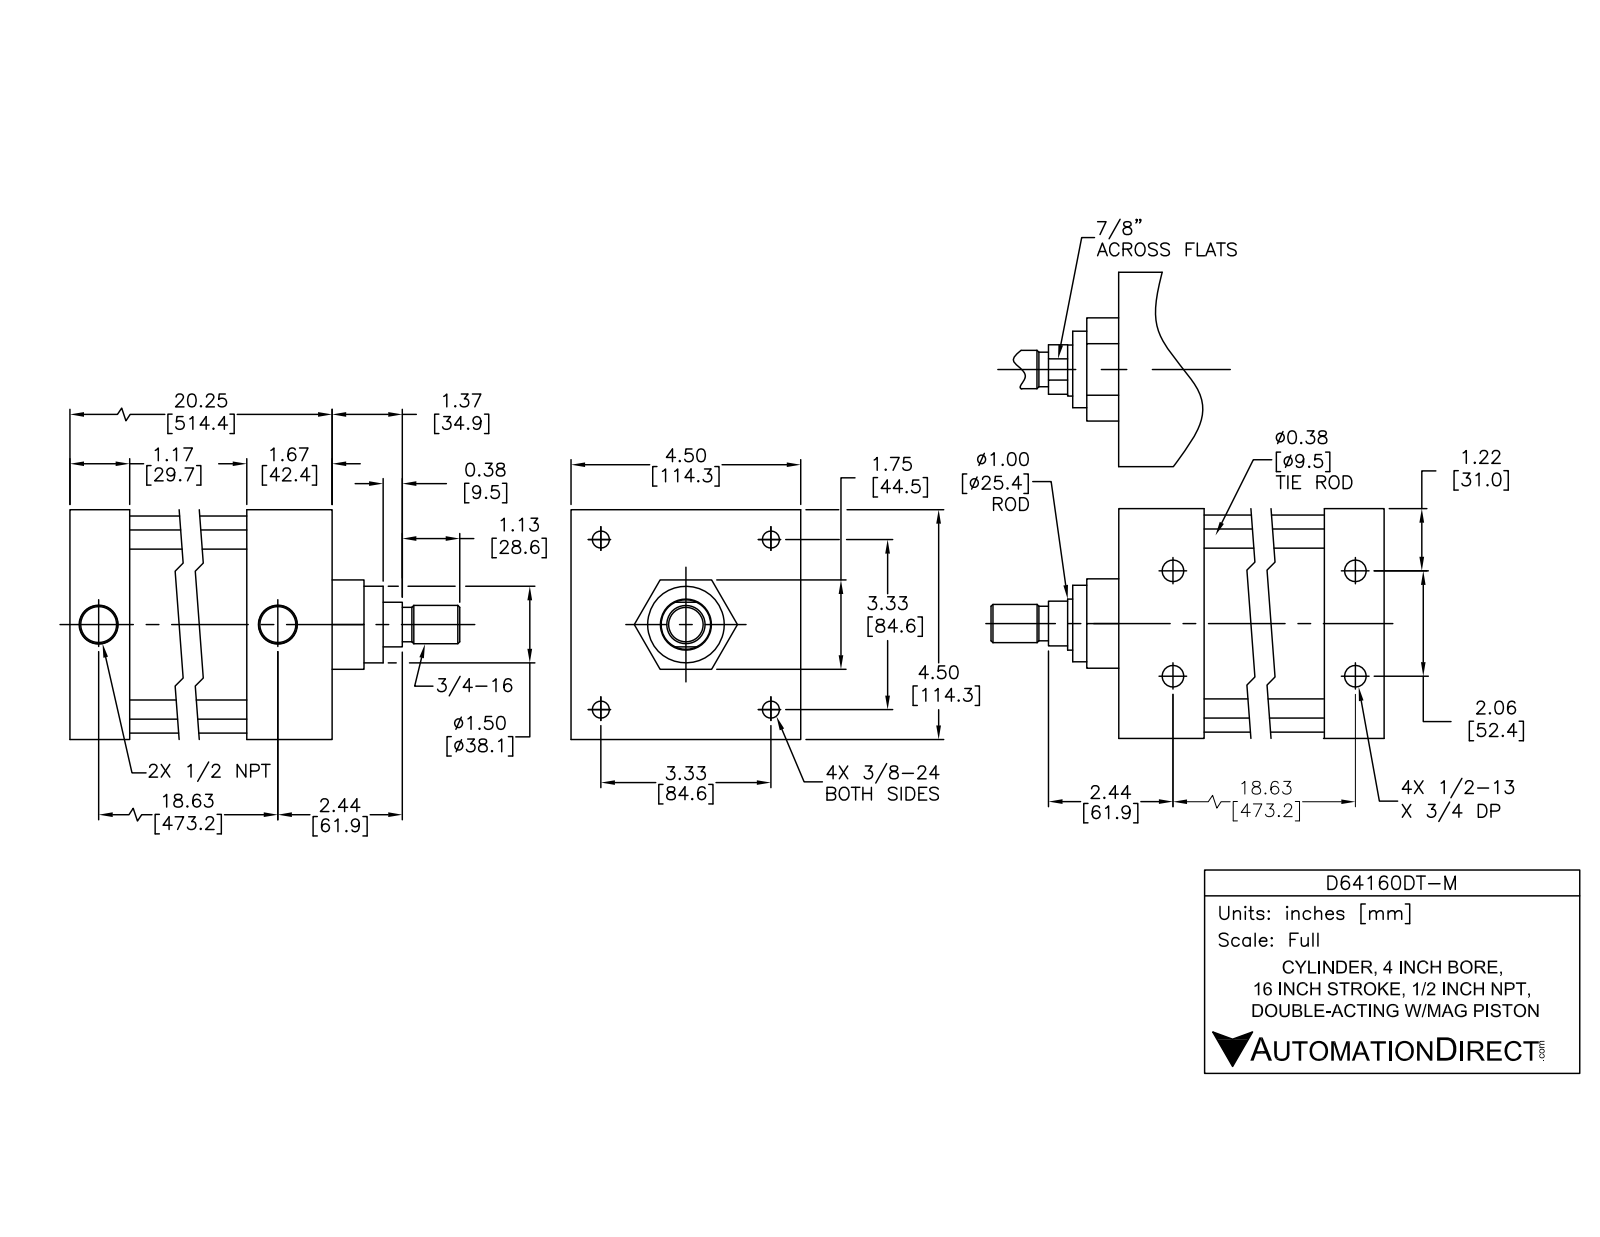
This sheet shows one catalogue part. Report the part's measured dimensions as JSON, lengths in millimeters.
{"part_name": "D64160DT-M; D64160DT-M PISTON; D64160DT-M BODY", "step_written_by": "SolidWorks 2015 (AUTOMOTIVE_DESIGN)", "units": "millimeters", "bodies": {"solids": 12, "faces": 303, "planar": 99, "cylindrical": 114, "other": 90}, "overall_size": [577.7, 114.3, 114.3], "volume_mm3": 1993000, "surface_area_mm2": 531300, "round_holes": [[8.4, 4], [10.3, 4], [10.6, 4], [15.9, 4], [12.7, 2], [19.5, 2], [25.4, 1], [25.5, 1], [101.6, 1]], "round_bosses_or_shafts": [[15.5, 4], [9.5, 4], [8.6, 4], [108, 1], [101.5, 1], [44.5, 1], [25.3, 1], [24.6, 1]], "partial_cylinders_radius": [[11.4, 4]], "face_to_face_distances": [114.3, 2, 440.1, 514.2, 44.5, 482.5, 31.7, 450.9, 31.6, 63.4], "hole_center_spacings": [59.7, 84.4, 473.7, 473, 26.2, 26.2, 52.4, 119.3]}
